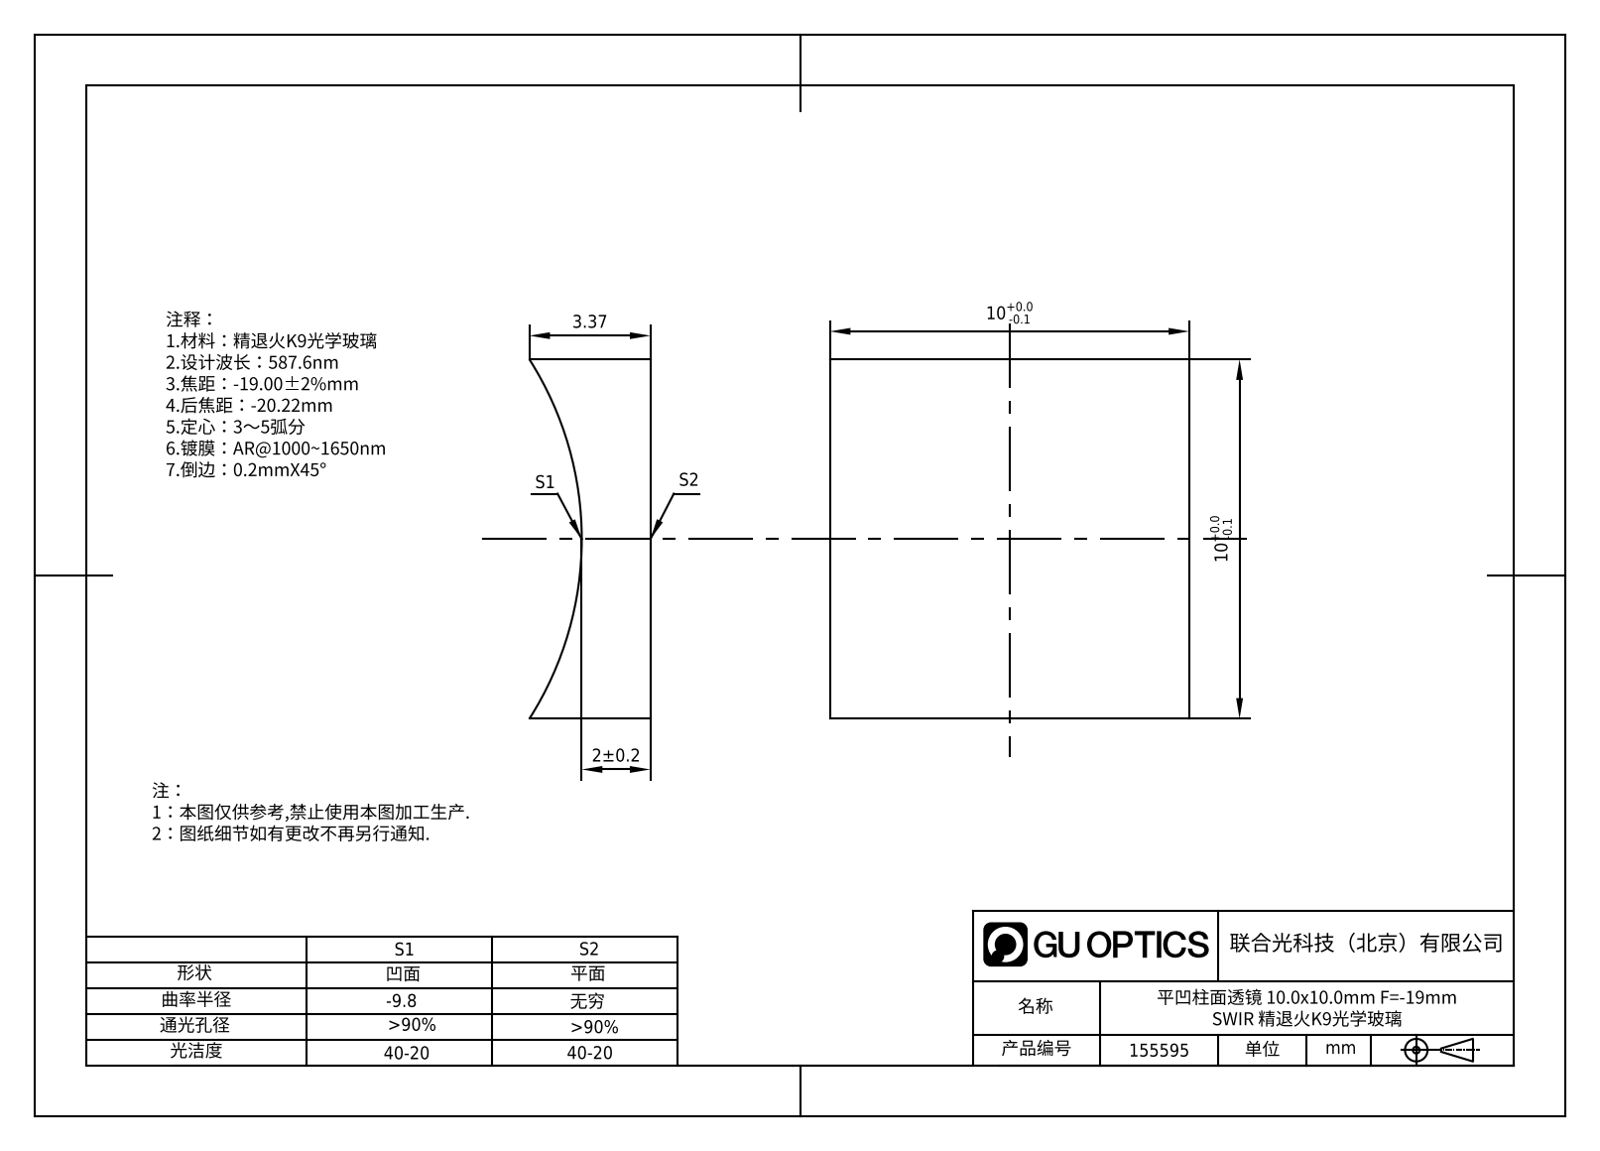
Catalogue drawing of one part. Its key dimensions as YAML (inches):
part_name: "155565"
step_written_by: "SolidWorks 2020 (CONFIG_CONTROL_DESIGN)"
units: inches
bodies: {solids: 1, faces: 6, planar: 5, cylindrical: 1, other: 0}
overall_size: [0.394, 0.394, 0.133]
volume: 0.015
surface_area: 0.498
partial_cylinders:
  - {radius: 0.366, count: 1}
face_to_face_distances: [0.394]
